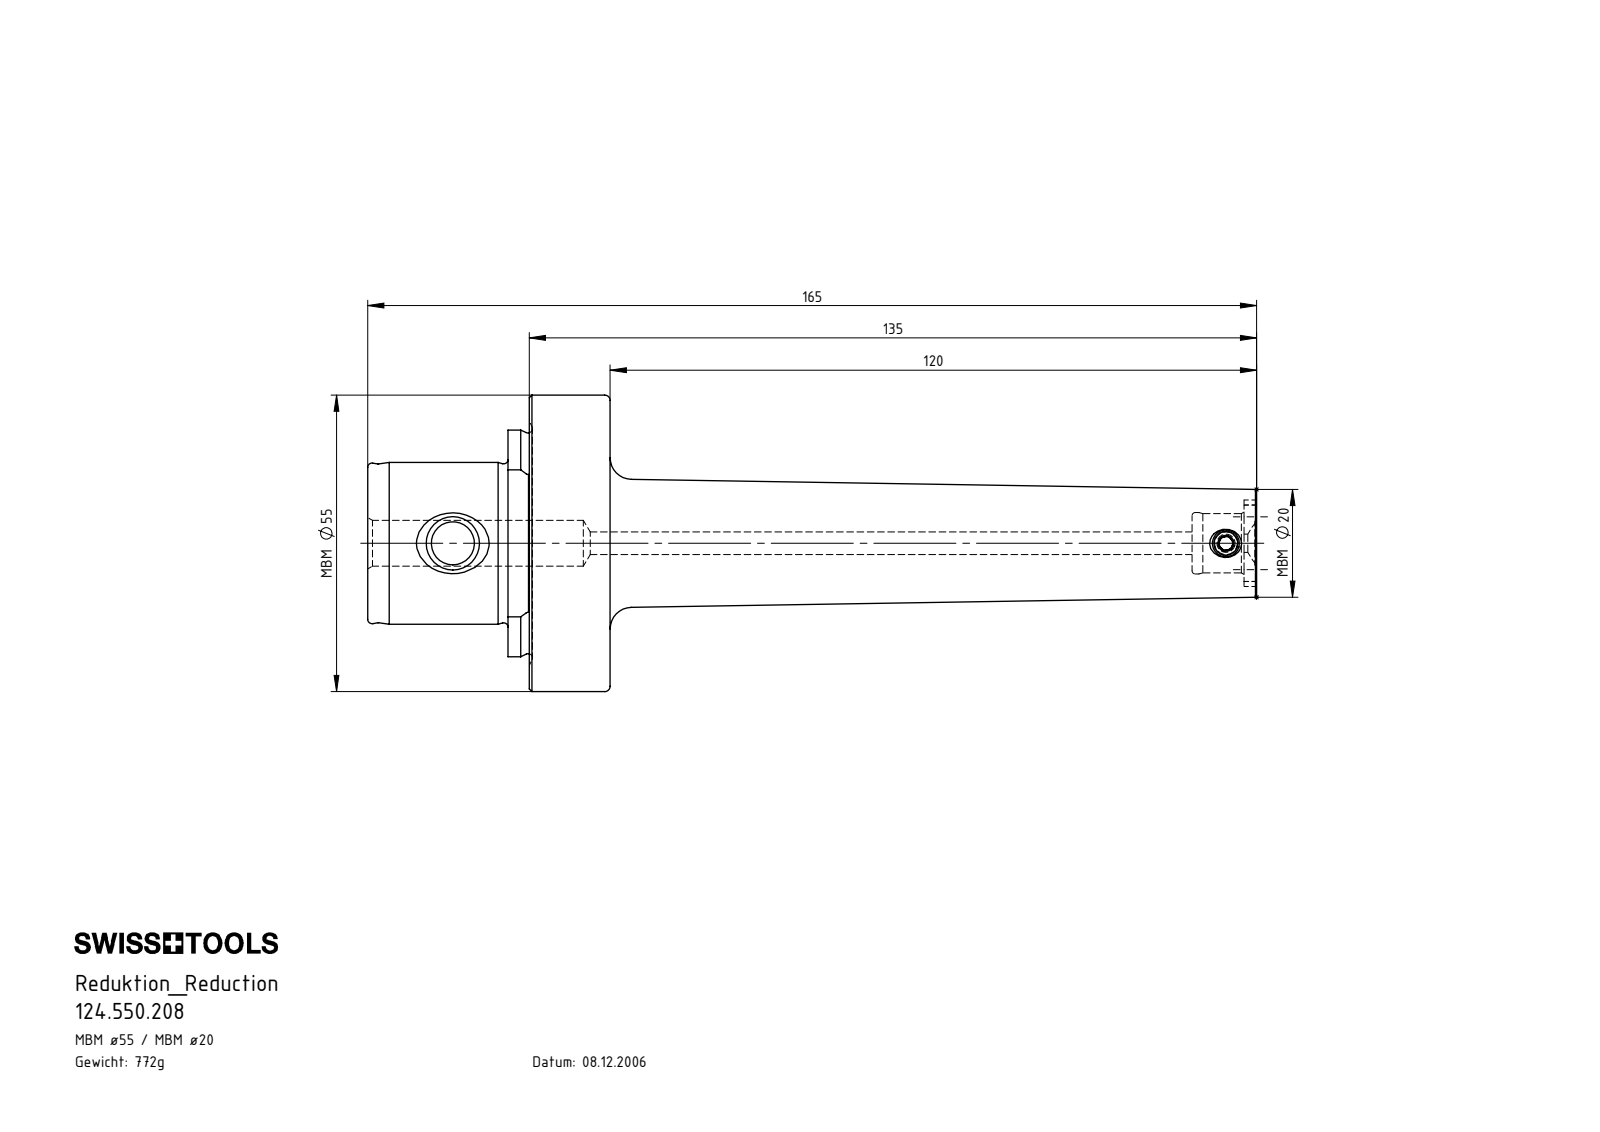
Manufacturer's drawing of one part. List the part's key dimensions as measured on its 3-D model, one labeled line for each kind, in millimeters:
Part name (STEP PRODUCT): 124.550.208; MB5-MB1.K01.135_C; MB1-ER1.001.006_A
STEP written by: SolidWorks 2017 (CONFIG_CONTROL_DESIGN)
Units: millimetres
Bodies: 2 solids, 139 faces (31 planar, 34 cylindrical, 74 other)
Overall size (bounding box): 165 × 55 × 55
Volume: 98 356 mm³ · Surface area: 21 497 mm²
Round holes (diameter × count): ⌀2.5 ×1, ⌀4.2 ×1, ⌀4.5 ×1, ⌀8 ×1, ⌀8.5 ×1, ⌀11 ×1, ⌀11.4 ×1
Round bosses / shafts (diameter × count): ⌀55 ×1, ⌀30 ×1, ⌀5 ×1
Partial cylindrical surfaces — rounded edges, fillets, slot ends (radius × count): R2.2 ×4, R6.5 ×1, R8.03 ×1, R21.02 ×1
Main face-to-face distances: 15, 30, 45, 26.05, 3.95, 18.95, 29.85, 3.8, 15.15, 32
Hole centre spacings: 143.5
